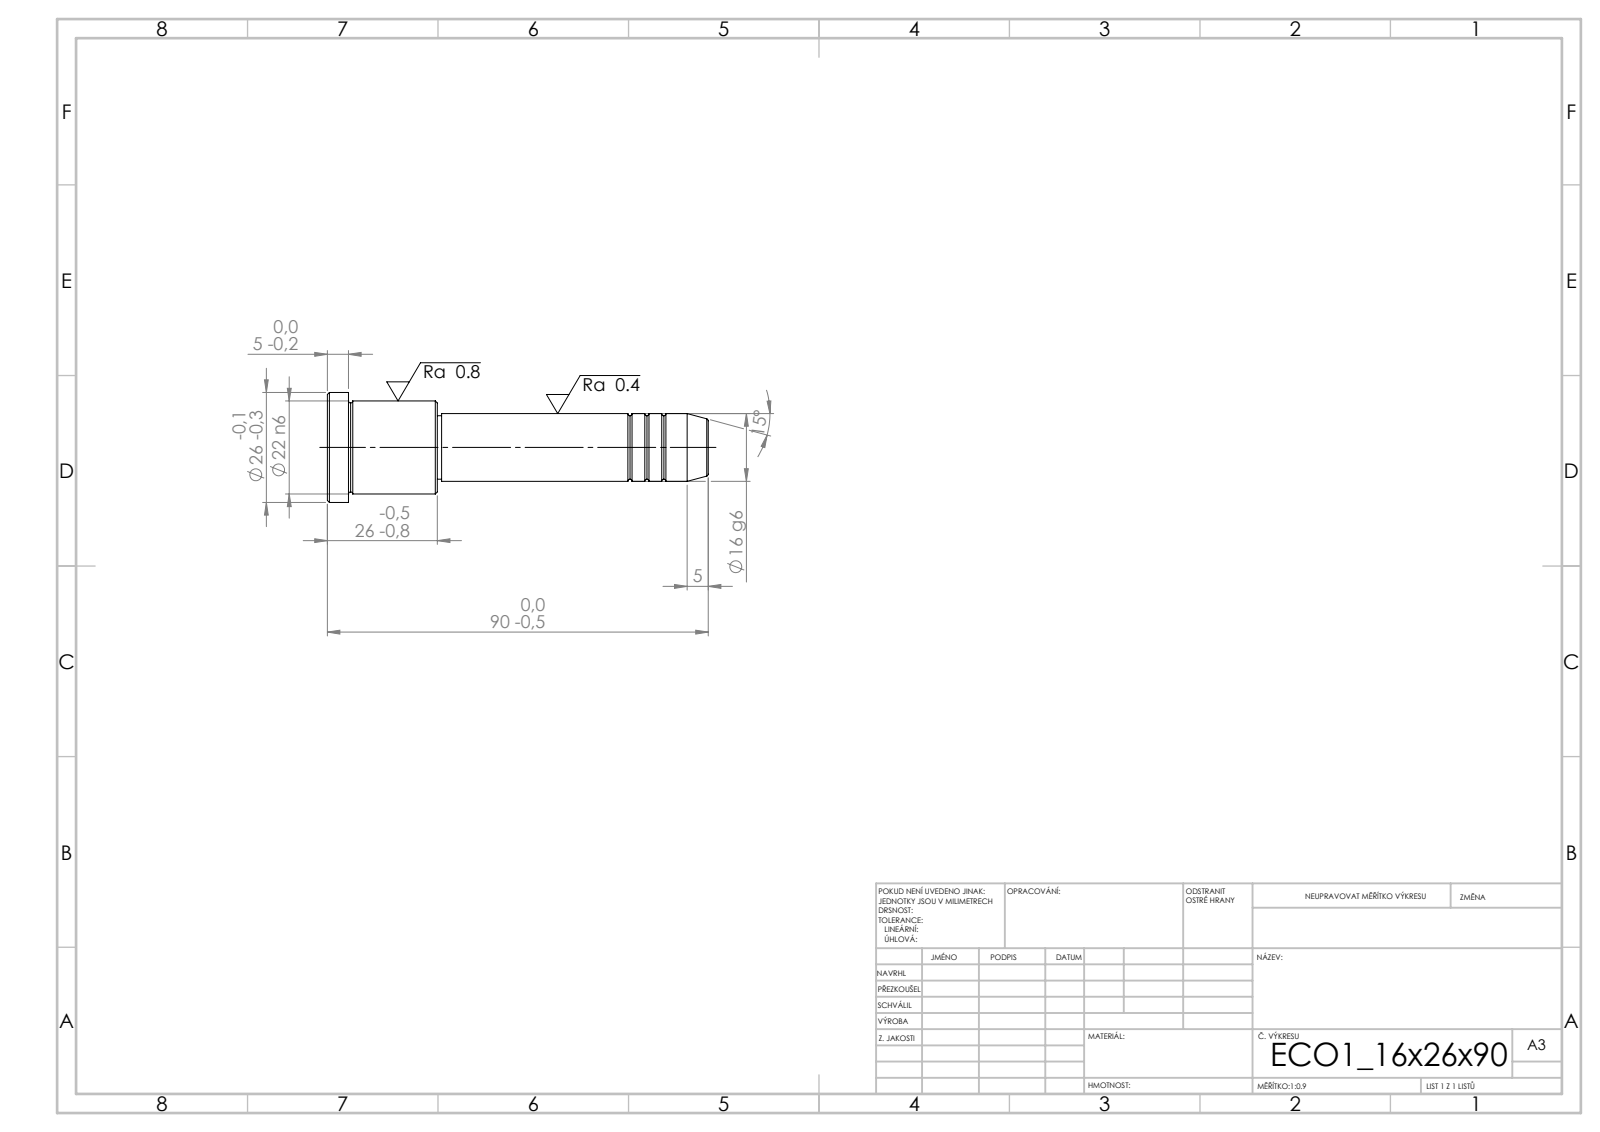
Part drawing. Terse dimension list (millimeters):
written by: SolidWorks 2019 (CONFIG_CONTROL_DESIGN)
unit: mm
bodies: 1 solid, 43 faces (5 planar, 14 cylindrical, 24 other)
size: 90 × 26 × 26
volume: 23 218 mm³; area: 6 173 mm²
bosses: 1× ⌀26, 1× ⌀22, 1× ⌀16, 1× ⌀15
face distances: 26, 21, 5, 64, 85, 90, 63, 1, 22, 27
